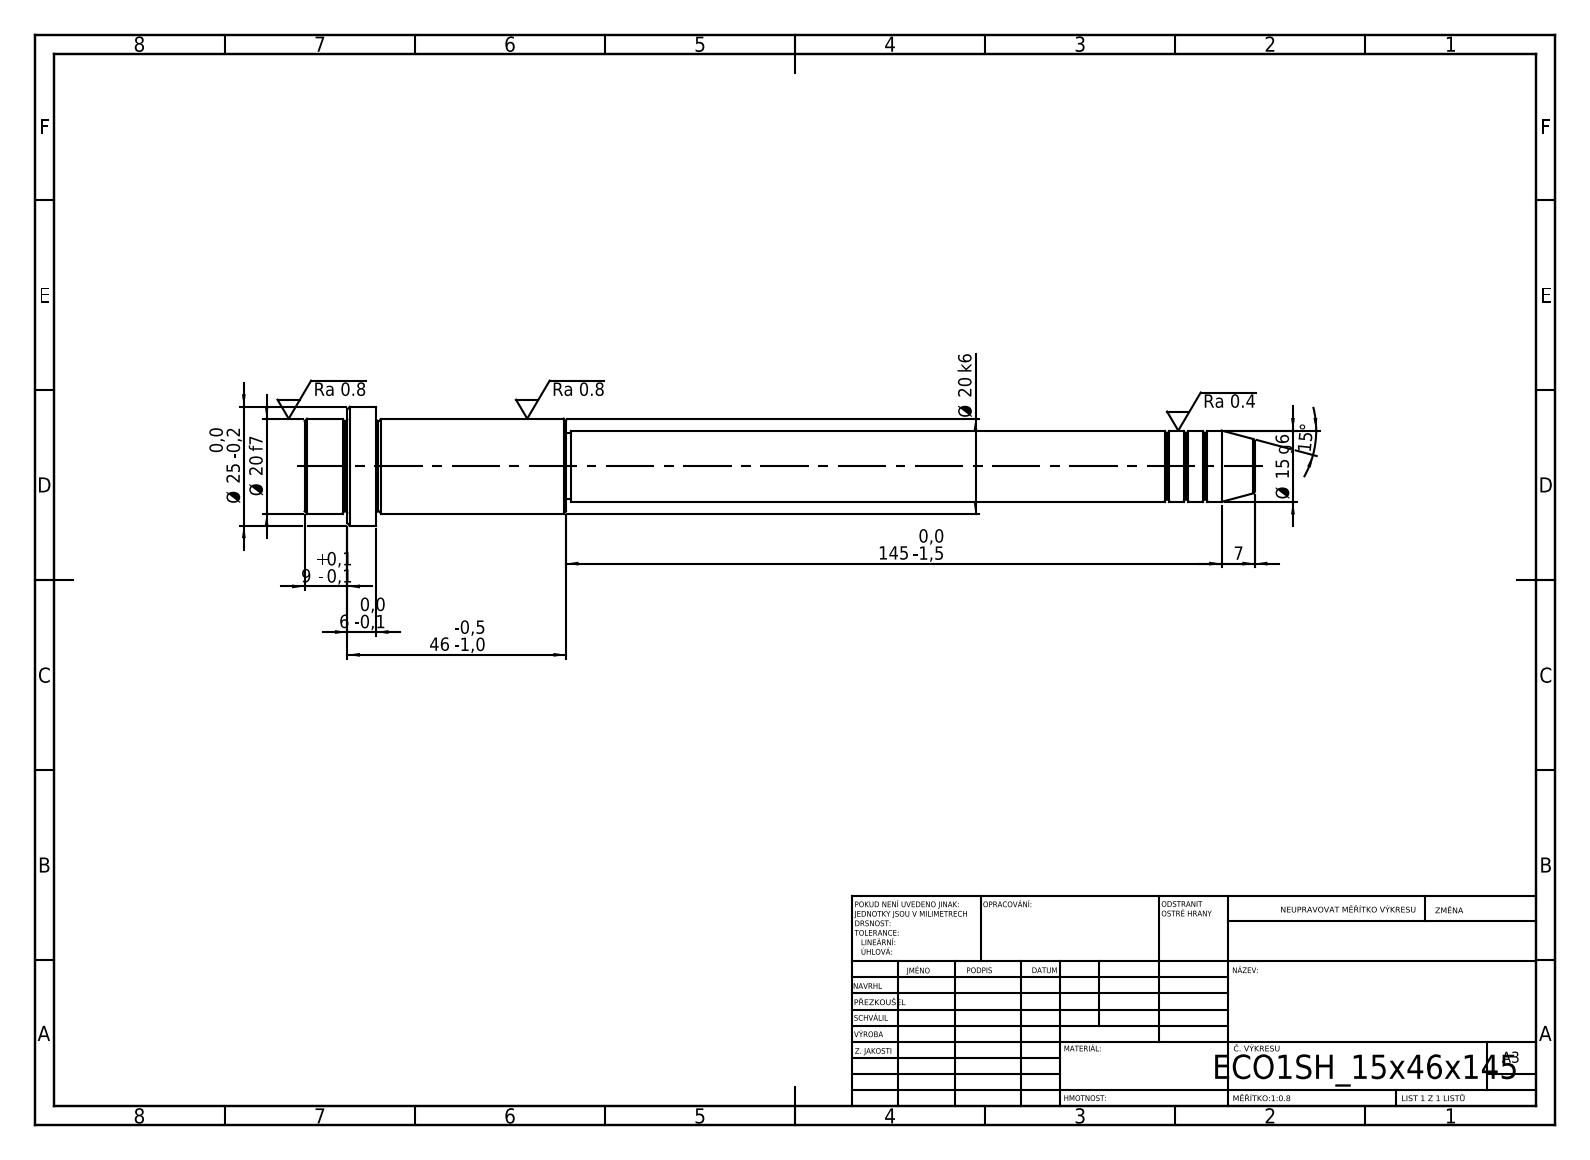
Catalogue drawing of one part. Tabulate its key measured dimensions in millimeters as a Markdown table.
| quantity | value |
| --- | --- |
| STEP written by | SolidWorks 2019 (CONFIG_CONTROL_DESIGN) |
| units | millimeters |
| bodies | 1 solid, 52 faces (6 planar, 16 cylindrical, 30 other) |
| overall size | 200 × 25 × 25 |
| volume | 43 528 mm³ |
| surface area | 11 371 mm² |
| round bosses / shafts (diameter × count) | 25 × 1, 20 × 1, 15 × 1, 14 × 1 |
| main face-to-face distances | 15, 6, 9, 40, 46, 55, 145, 185, 191, 200 |
